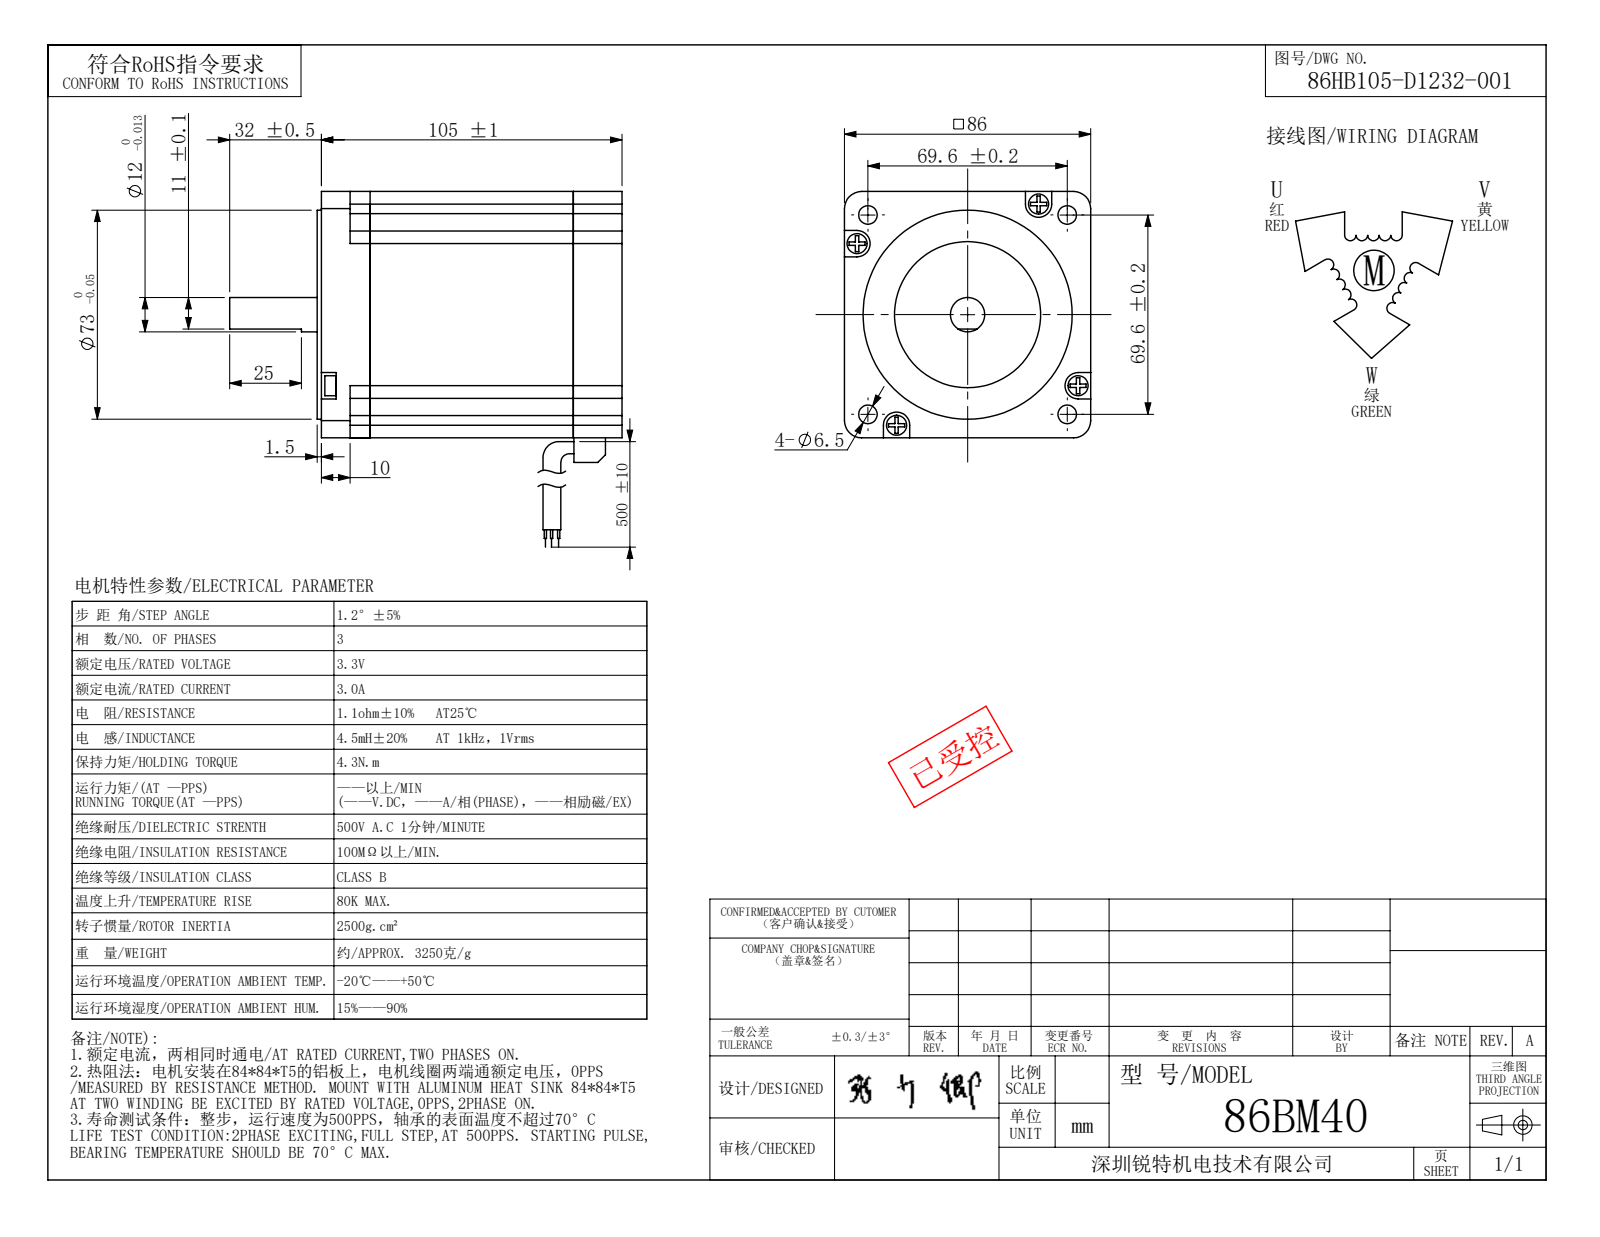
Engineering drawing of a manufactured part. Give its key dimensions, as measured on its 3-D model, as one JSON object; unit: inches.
{"part_name": "86BM40 (86HB105-D1232-001)", "step_written_by": "SolidWorks 2020 (AUTOMOTIVE_DESIGN)", "units": "inches", "bodies": {"solids": 7, "faces": 269, "planar": 139, "cylindrical": 122, "other": 8}, "overall_size": [5.394, 3.386, 3.386], "volume_in3": 19.13, "surface_area_in2": 149.7, "round_holes": [[0.173, 8], [0.256, 4], [1.575, 1], [2.008, 1], [3.181, 1]], "round_bosses_or_shafts": [[0.276, 4], [2.874, 1], [2.047, 1], [0.472, 1]], "partial_cylinders_radius": [[0.173, 9], [0.181, 4], [0.236, 4], [0.238, 4], [0.174, 1]], "face_to_face_distances": [3.386, 0.669, 3.465, 4.134, 3.74, 3.071, 0.394, 0.276, 2.795, 0.543], "hole_center_spacings": [0.421, 1.806, 2.351, 2.554, 2.917, 3.722, 0.769, 1.937]}
